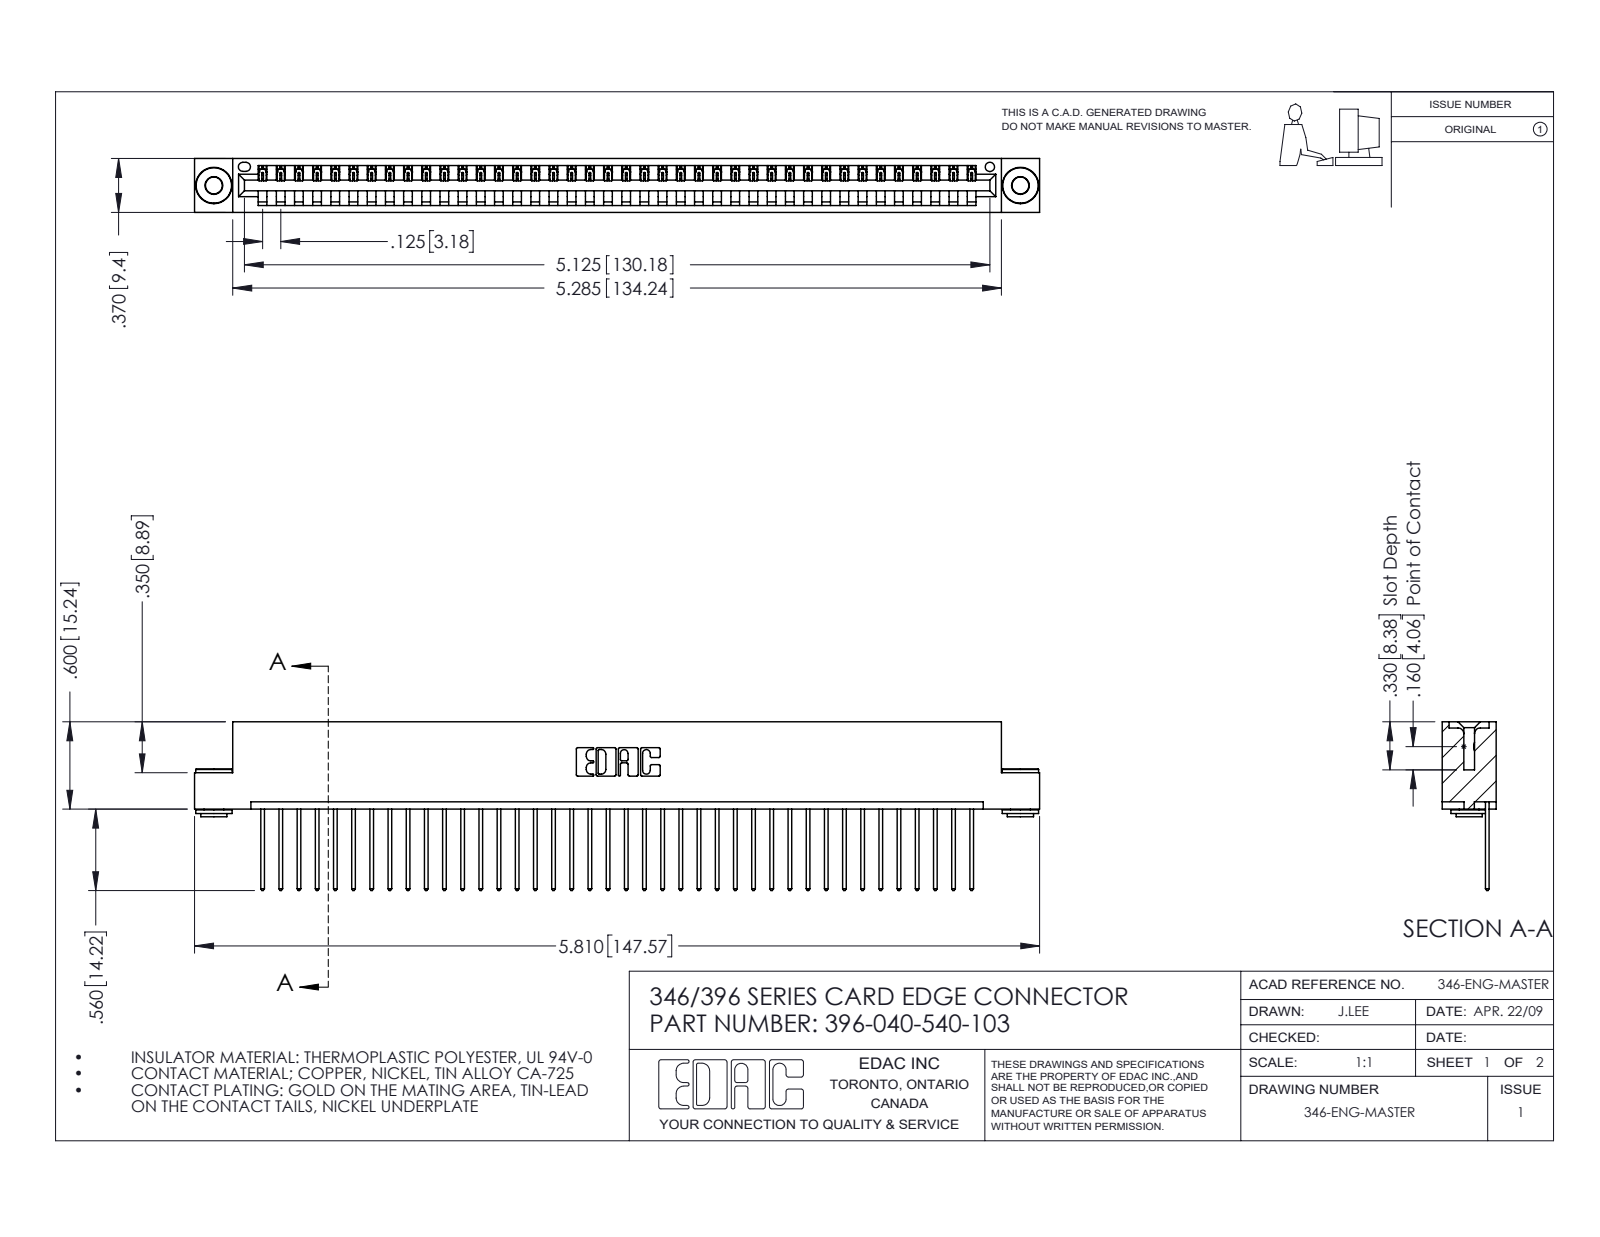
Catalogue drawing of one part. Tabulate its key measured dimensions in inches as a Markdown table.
| quantity | value |
| --- | --- |
| part name | 346 Part_Flush Mounting Lugs - 0.156 Dia-TH; 345-292-001_345-293-140; 396-040-540-103; 345-250-002_345-250-002-102 |
| STEP written by | SolidWorks 2016 (CONFIG_CONTROL_DESIGN) |
| units | inches |
| bodies | 43 solids, 2480 faces (1686 planar, 786 cylindrical, 8 other) |
| overall size | 5.81 × 1.16 × 0.37 |
| volume | 0.866 in³ |
| surface area | 28.4 in² |
| round holes (diameter × count) | 0.116 × 2, 0.156 × 2, 0.064 × 1 |
| round bosses / shafts (diameter × count) | 0.25 × 2, 0.18 × 2, 0.136 × 2 |
| partial cylindrical surfaces (radius × count) | 0.006 × 80, 0.01 × 80, 0.01 × 22, 0.007 × 6, 0.031 × 6, 0.026 × 3, 0.031 × 2, 0.04 × 2 |
| main face-to-face distances | 0.048, 0.322, 0.37, 0.25, 0.025, 0.072, 0.298, 0.148, 0.222, 0.1 |
| hole center spacings | 0.246, 5.336, 5.545 |
